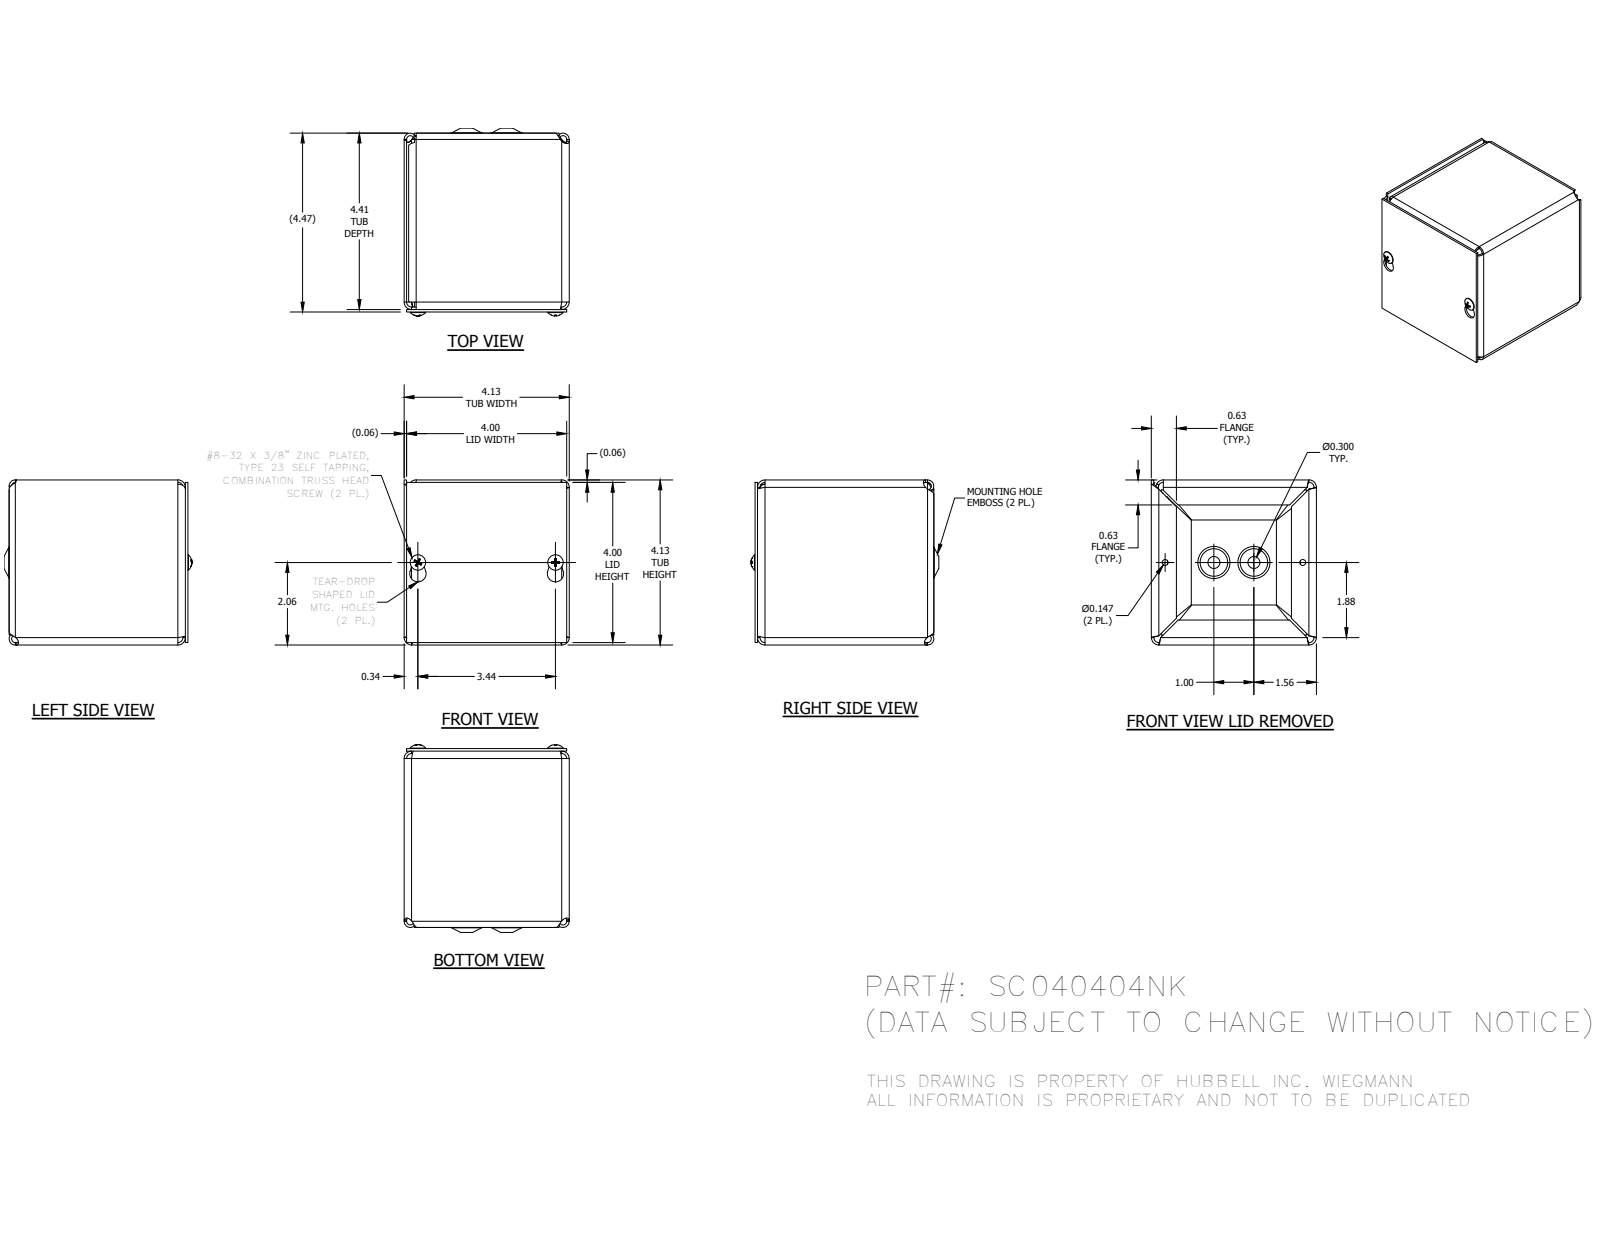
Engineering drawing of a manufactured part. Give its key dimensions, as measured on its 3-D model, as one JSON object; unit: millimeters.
{"part_name": "SC0404BKP; SC040404NKWRA; SC0404LID; 34056 (+1 more)", "step_written_by": "Autodesk Inventor 2014 (AUTOMOTIVE_DESIGN)", "units": "millimeters", "bodies": {"solids": 5, "faces": 274, "planar": 107, "cylindrical": 53, "other": 114}, "overall_size": [119.2, 104.78, 104.78], "volume_mm3": 120030, "surface_area_mm2": 155830, "round_holes": [[3.73, 2], [7.62, 2]], "round_bosses_or_shafts": [[9.75, 2], [4.17, 2]], "partial_cylinders_radius": [[3.17, 10], [4.75, 8], [1.4, 4], [1.57, 4], [2.38, 4], [2.97, 4], [3.15, 4], [3.96, 4]], "face_to_face_distances": [1.57, 103.2, 101.63, 110.32, 1.58, 111.89, 104.78, 103.21, 104.77, 1.59], "hole_center_spacings": [25.4, 30.95, 30.96, 56.35, 56.36, 87.31]}
